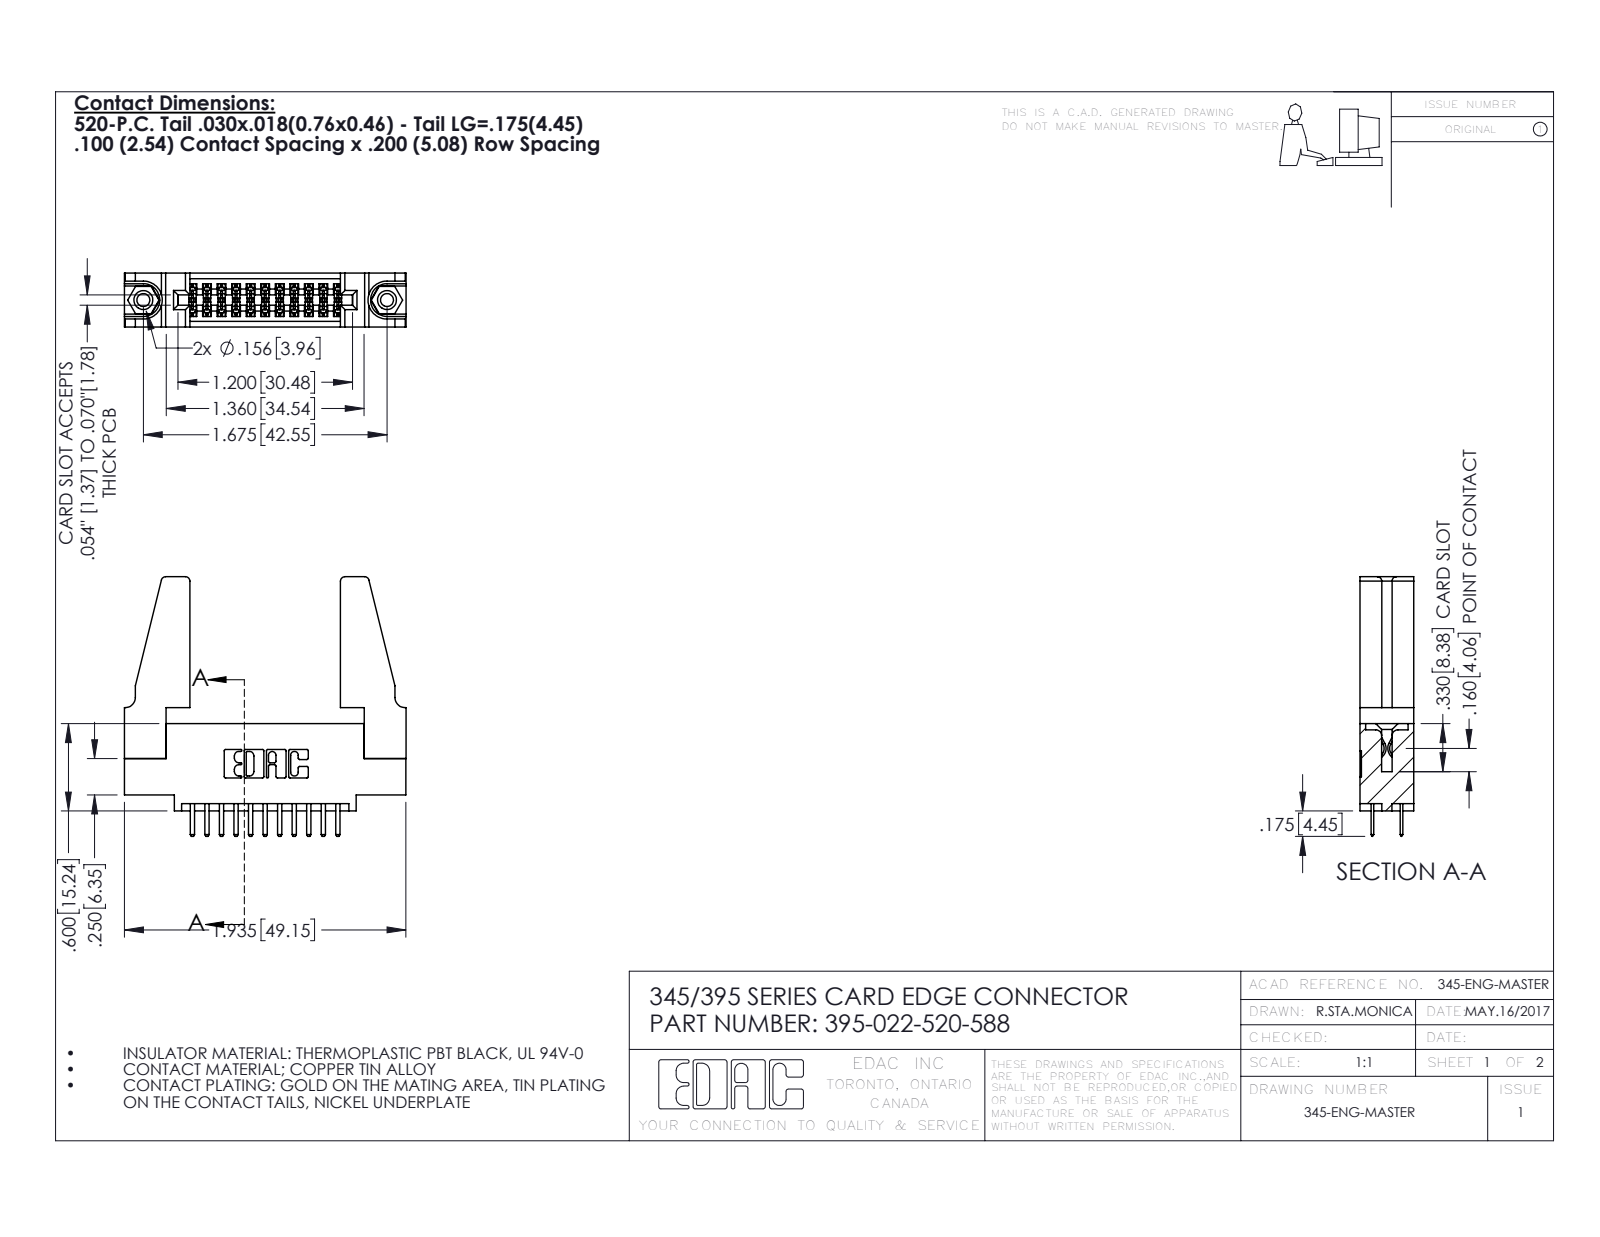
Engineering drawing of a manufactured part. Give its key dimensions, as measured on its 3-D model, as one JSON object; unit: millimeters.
{"part_name": "345-250-001_345-250-001-102; 345 Part_0.110 Offset - 0.156 Dia-TH; 395-022-520-588; 345-292-001_345-293-120 (+1 more)", "step_written_by": "SolidWorks 2016 (CONFIG_CONTROL_DESIGN)", "units": "millimeters", "bodies": {"solids": 27, "faces": 1442, "planar": 926, "cylindrical": 500, "other": 16}, "overall_size": [49.2, 45.3, 9.4], "volume_mm3": 7650, "surface_area_mm2": 9110, "round_holes": [[2.3, 2], [3.2, 2], [4, 2], [1.6, 1]], "round_bosses_or_shafts": [[3.9, 2]], "partial_cylinders_radius": [[0.2, 33], [0.3, 26], [0.3, 22], [0.8, 8], [0.2, 6], [0.8, 6], [0.7, 3], [0.4, 2]], "face_to_face_distances": [9.4, 1.8, 7.6, 5.1, 5.7, 2.5, 6.9, 0.6, 15.2, 3.8], "hole_center_spacings": [6.9, 36.7, 42.5]}
